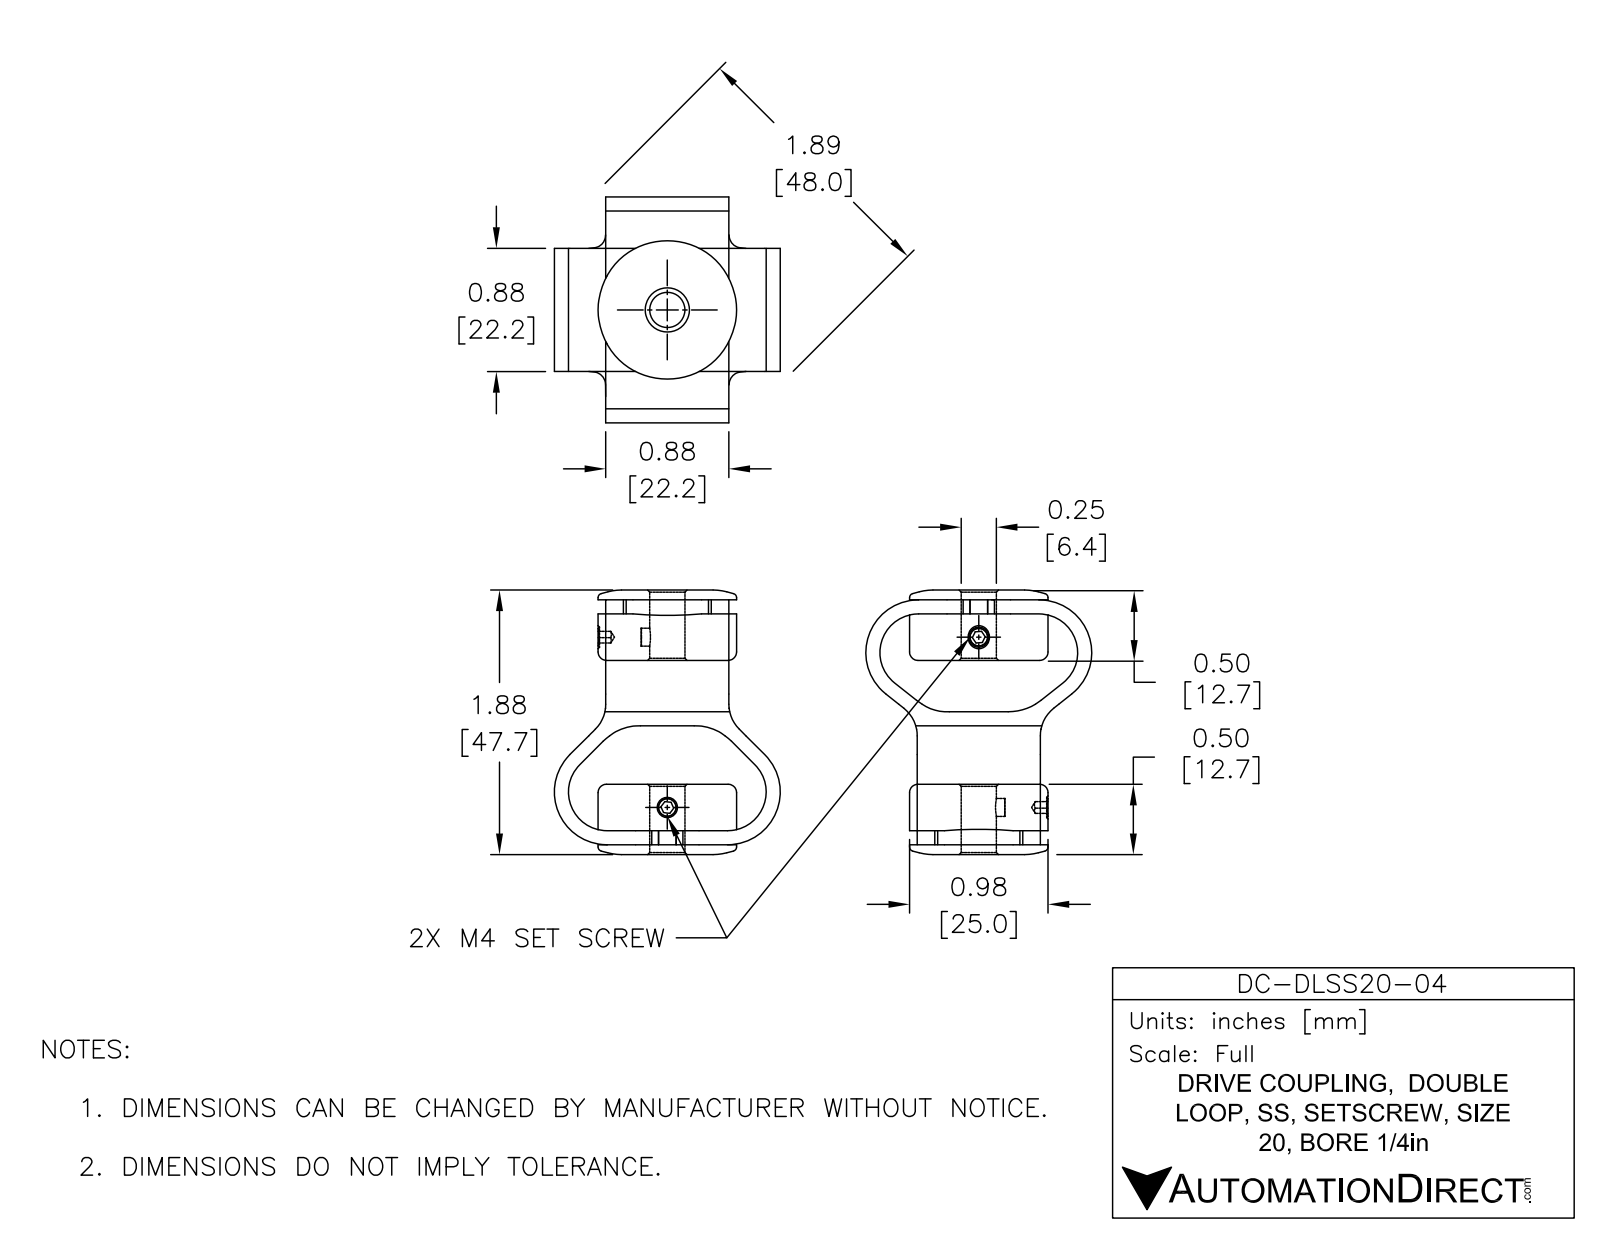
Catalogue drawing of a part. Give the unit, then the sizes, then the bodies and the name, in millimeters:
Units: millimetres
Overall size (bounding box): 47.75 × 40.77 × 40.77
Round holes (diameter × count): ⌀3.24 ×2, ⌀6.35 ×1
Round bosses / shafts (diameter × count): ⌀25 ×1
Partial cylindrical surfaces — rounded edges, fillets, slot ends (radius × count): R9.53 ×7, R6.35 ×6, R6.99 ×4, R1.91 ×3, R1.91 ×1, R7.94 ×1
Main face-to-face distances: 2.54, 12.7, 35.05, 22.35, 13.08, 9.27, 1.78, 45.97, 10.92, 33.27
Volume: 18 624 mm³ · Surface area: 11 269 mm²
Bodies: 1 solid, 173 faces (90 planar, 47 cylindrical, 36 other)
Part name (STEP PRODUCT): DC-DLSS20-04
STEP written by: SolidWorks 2015 (AUTOMOTIVE_DESIGN)
